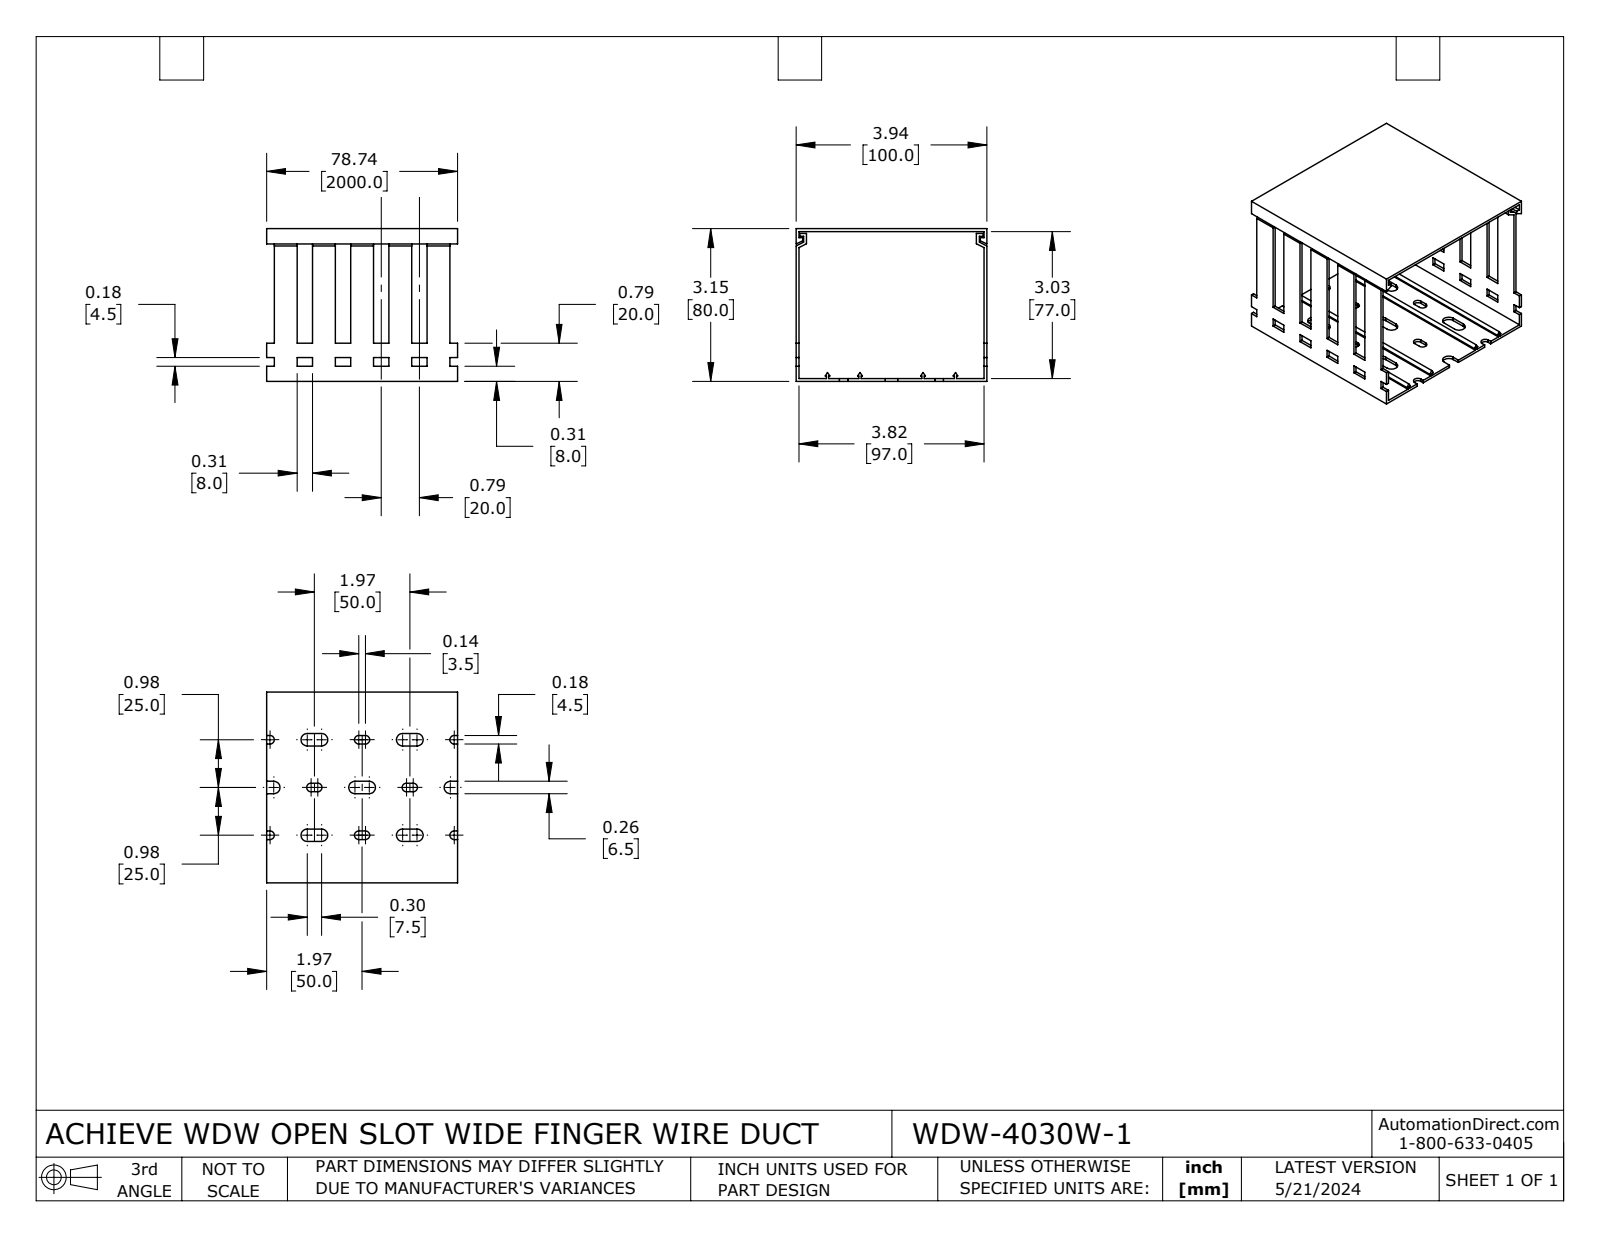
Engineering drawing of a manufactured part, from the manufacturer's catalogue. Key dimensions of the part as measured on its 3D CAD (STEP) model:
Part name (STEP PRODUCT): WDW-4030W-1
STEP written by: SolidWorks 2023 (CONFIG_CONTROL_DESIGN)
Units: millimetres
Bodies: 2 solids, 272 faces (236 planar, 36 cylindrical, 0 other)
Overall size (bounding box): 100 × 100 × 80
Volume: 49 322 mm³ · Surface area: 70 248 mm²
Partial cylindrical surfaces — rounded edges, fillets, slot ends (radius × count): R2.25 ×12, R3.25 ×12
Main face-to-face distances: 1.5, 78.5, 98.5, 80, 77, 100, 97, 20, 4, 40
